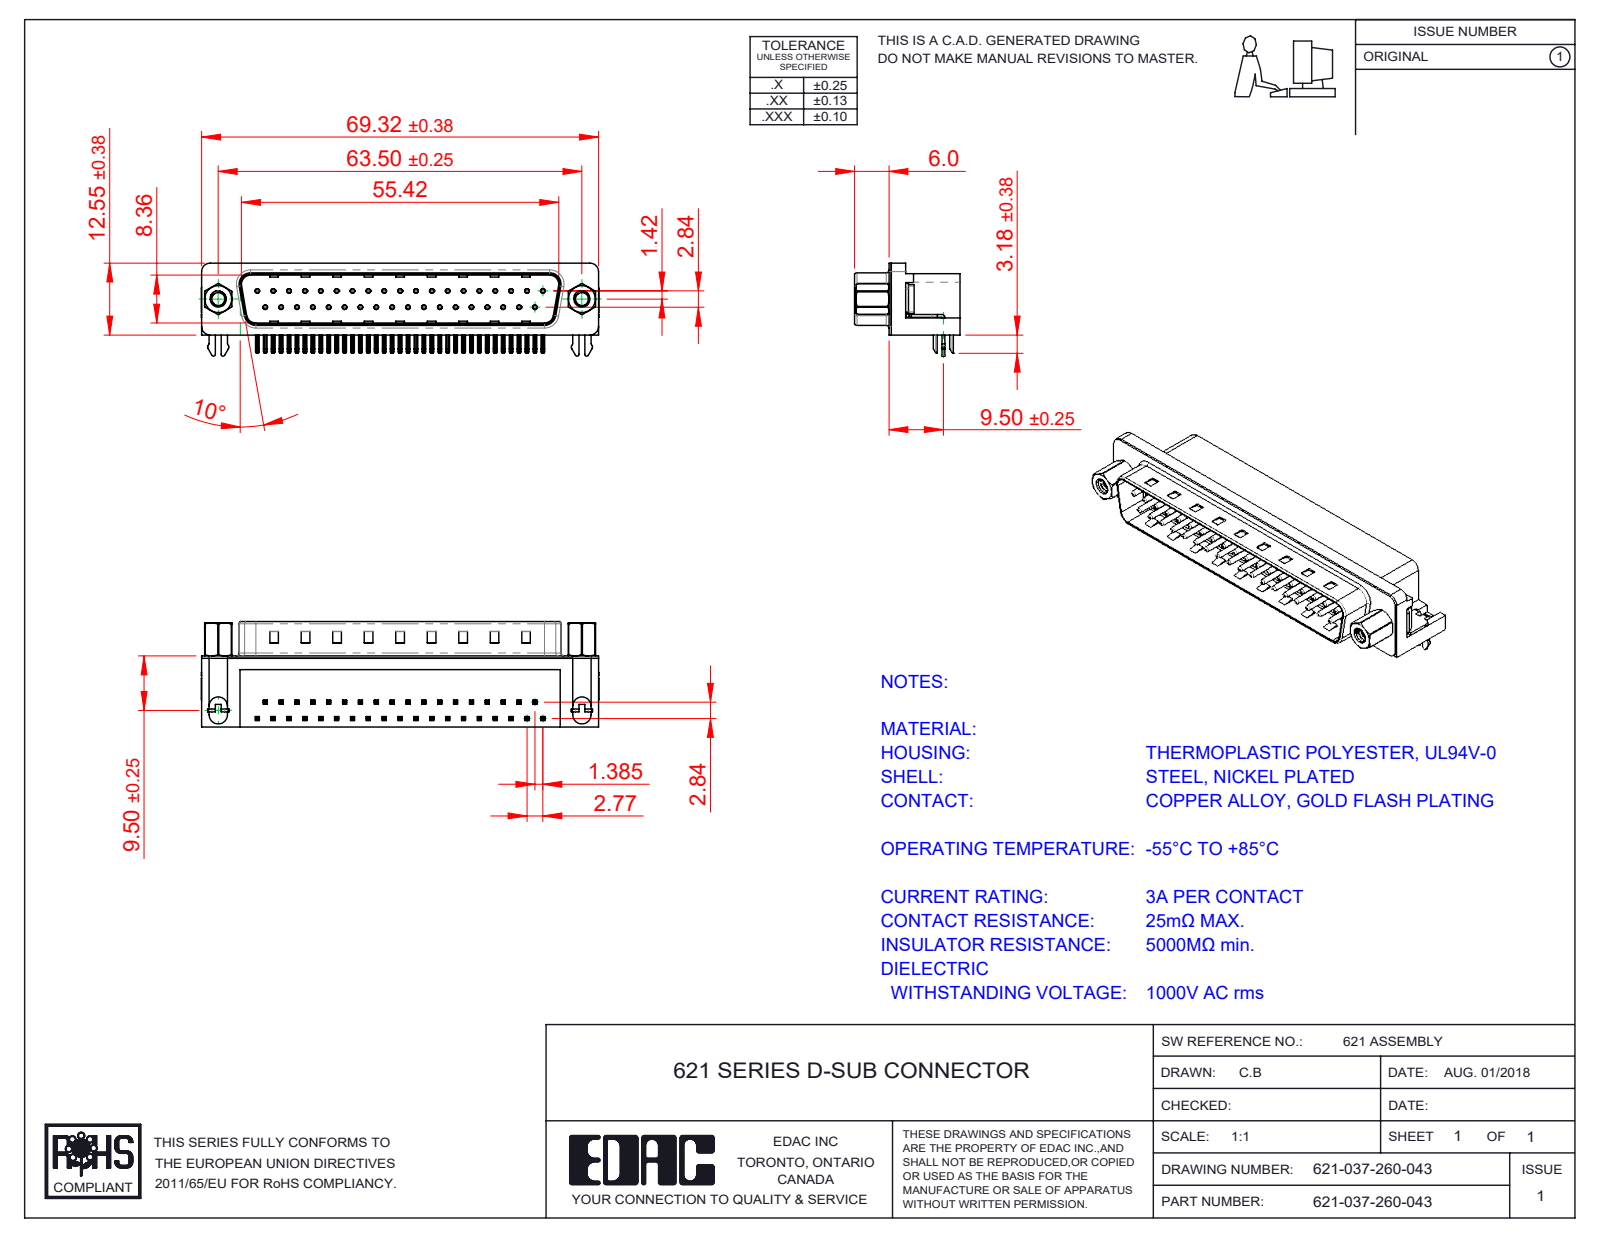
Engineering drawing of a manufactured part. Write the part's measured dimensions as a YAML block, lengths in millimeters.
part_name: "621 Shell_37 Socket; 621 4 Prong Board Lock; 621 4-40 Hex Standoff 5; 621 Housing_37 Socket (+4 more)"
step_written_by: "SolidWorks 2016 (CONFIG_CONTROL_DESIGN)"
units: millimeters
bodies: {solids: 45, faces: 3445, planar: 2077, cylindrical: 993, other: 375}
overall_size: [69.4, 18.4, 16.25]
volume: 8844
surface_area: 10652
round_holes:
  - {diameter: 0.35, count: 37}
  - {diameter: 0.8, count: 37}
  - {diameter: 2, count: 2}
  - {diameter: 2.26, count: 2}
  - {diameter: 2.29, count: 2}
  - {diameter: 4, count: 2}
  - {diameter: 4.8, count: 2}
  - {diameter: 5, count: 2}
round_bosses_or_shafts:
  - {diameter: 0.75, count: 37}
  - {diameter: 4.9, count: 2}
  - {diameter: 4.75, count: 2}
  - {diameter: 3.9, count: 2}
  - {diameter: 3, count: 2}
  - {diameter: 2.79, count: 2}
partial_cylinders:
  - {radius: 0.25, count: 160}
  - {radius: 0.12, count: 74}
  - {radius: 1, count: 16}
  - {radius: 0.5, count: 9}
  - {radius: 1.6, count: 8}
  - {radius: 1.5, count: 7}
  - {radius: 0.9, count: 4}
  - {radius: 2, count: 4}
face_to_face_distances: [0.4, 12, 10.35, 8.76, 2.1, 1.7, 10.46, 10.86, 12.4, 9]
hole_center_spacings: [3.16, 2.77, 5.54, 8.31, 11.08, 13.85, 19.39, 22.16]
